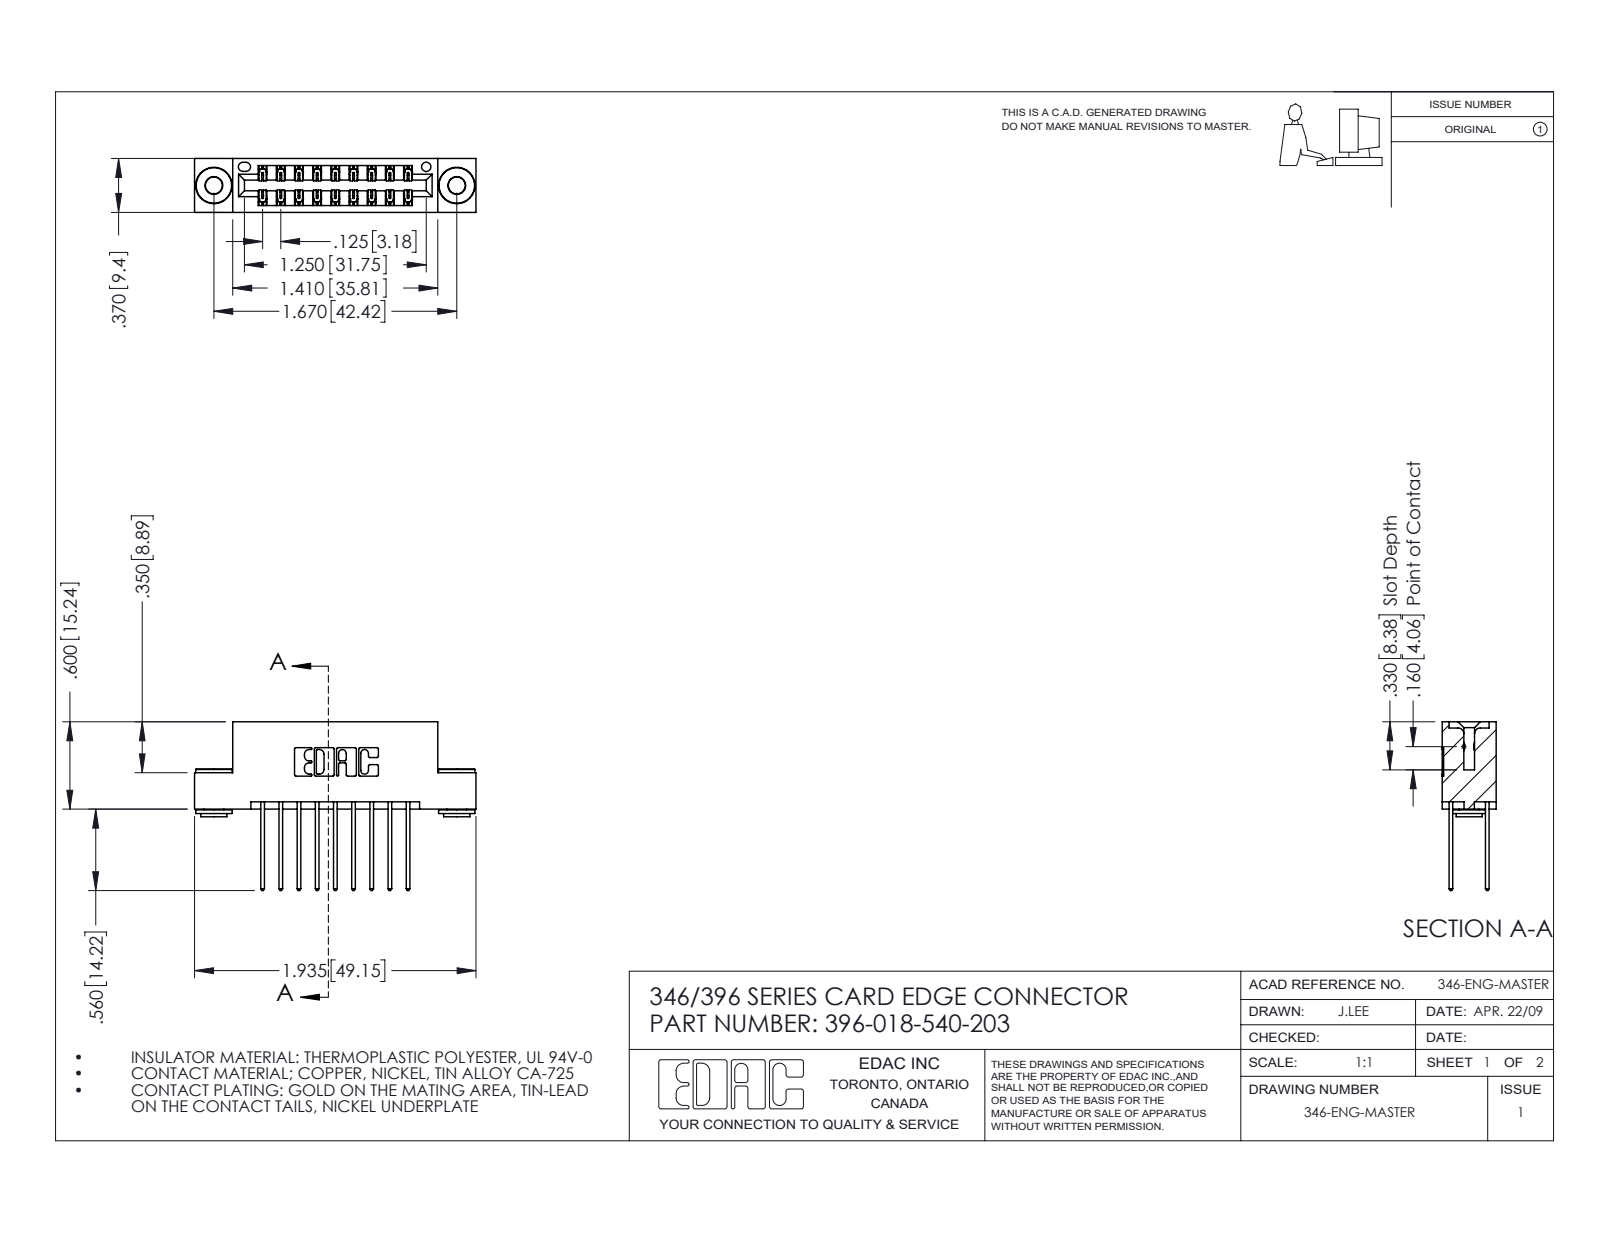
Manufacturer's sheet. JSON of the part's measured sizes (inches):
{"part_name": "396-018-540-203; 345-292-001_345-293-140; 345-250-002_345-250-002-102; 346 Part_Flush Mounting Lugs - 0.156 Dia-TH", "step_written_by": "SolidWorks 2016 (CONFIG_CONTROL_DESIGN)", "units": "inches", "bodies": {"solids": 21, "faces": 1096, "planar": 716, "cylindrical": 372, "other": 8}, "overall_size": [1.935, 1.16, 0.37], "volume_in3": 0.282, "surface_area_in2": 9.88, "round_holes": [[0.116, 2], [0.156, 2], [0.064, 1]], "round_bosses_or_shafts": [[0.25, 2], [0.18, 2], [0.136, 2]], "partial_cylinders_radius": [[0.006, 27], [0.01, 22], [0.01, 18], [0.007, 6], [0.031, 6], [0.026, 3], [0.014, 2], [0.022, 2]], "face_to_face_distances": [0.25, 0.048, 0.322, 0.37, 0.025, 0.072, 0.298, 0.275, 0.148, 0.222], "hole_center_spacings": [0.246, 1.465, 1.67]}
